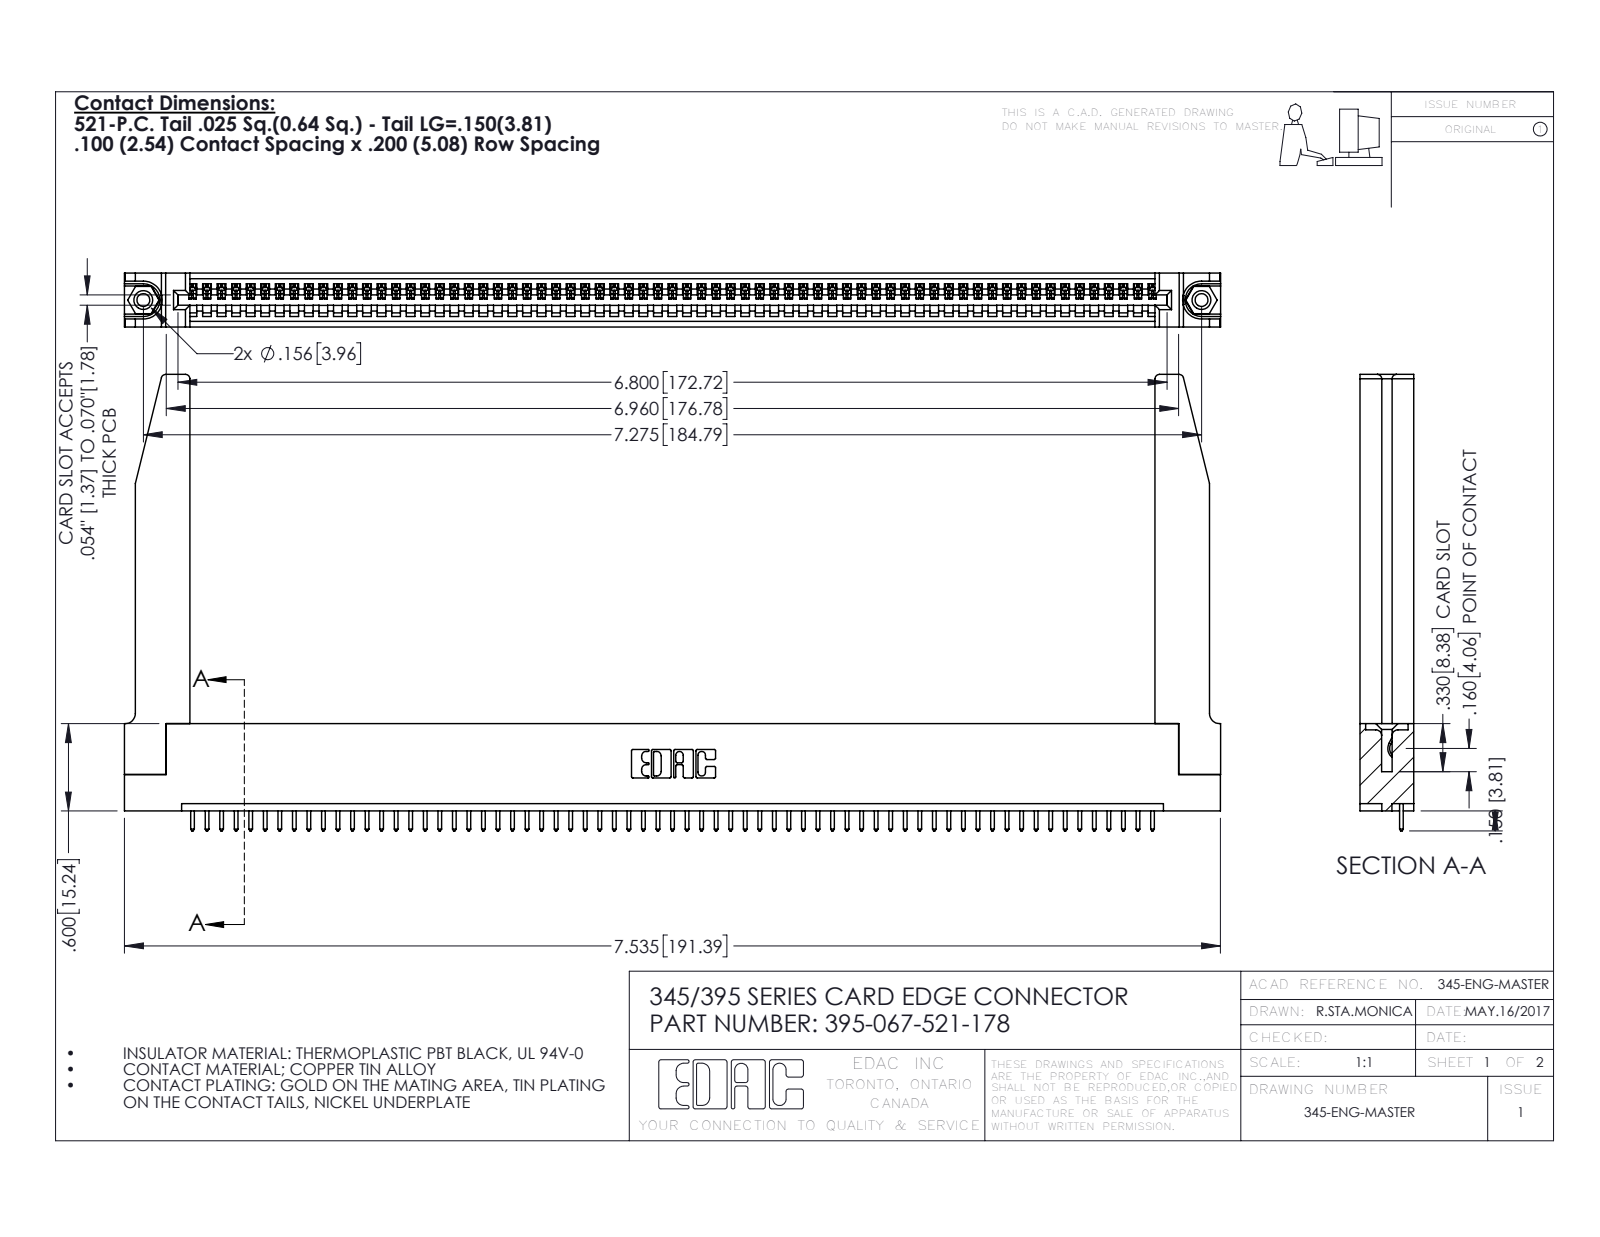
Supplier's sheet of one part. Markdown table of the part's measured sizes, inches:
| quantity | value |
| --- | --- |
| part name | 345 Part_Flush Mounting Lugs - 0.156 Dia-TH; 345-292-001_345-293-121; 395-067-521-178; 345-220-078_345-220-078 (+1 more) |
| STEP written by | SolidWorks 2016 (CONFIG_CONTROL_DESIGN) |
| units | inches |
| bodies | 72 solids, 4246 faces (2902 planar, 1292 cylindrical, 52 other) |
| overall size | 7.536 × 3.137 × 0.37 |
| volume | 1.585 in³ |
| surface area | 47.46 in² |
| round holes (diameter × count) | 0.089 × 2, 0.125 × 2, 0.156 × 2, 0.064 × 1 |
| round bosses / shafts (diameter × count) | 0.155 × 2 |
| partial cylindrical surfaces (radius × count) | 0.006 × 134, 0.01 × 134, 0.01 × 22, 0.03 × 8, 0.007 × 6, 0.031 × 6, 0.026 × 3, 0.031 × 2 |
| main face-to-face distances | 0.072, 0.37, 0.298, 0.2, 0.098, 0.272, 0.025, 0.225, 0.149, 0.148 |
| hole center spacings | 0.27, 7.039, 7.275 |
